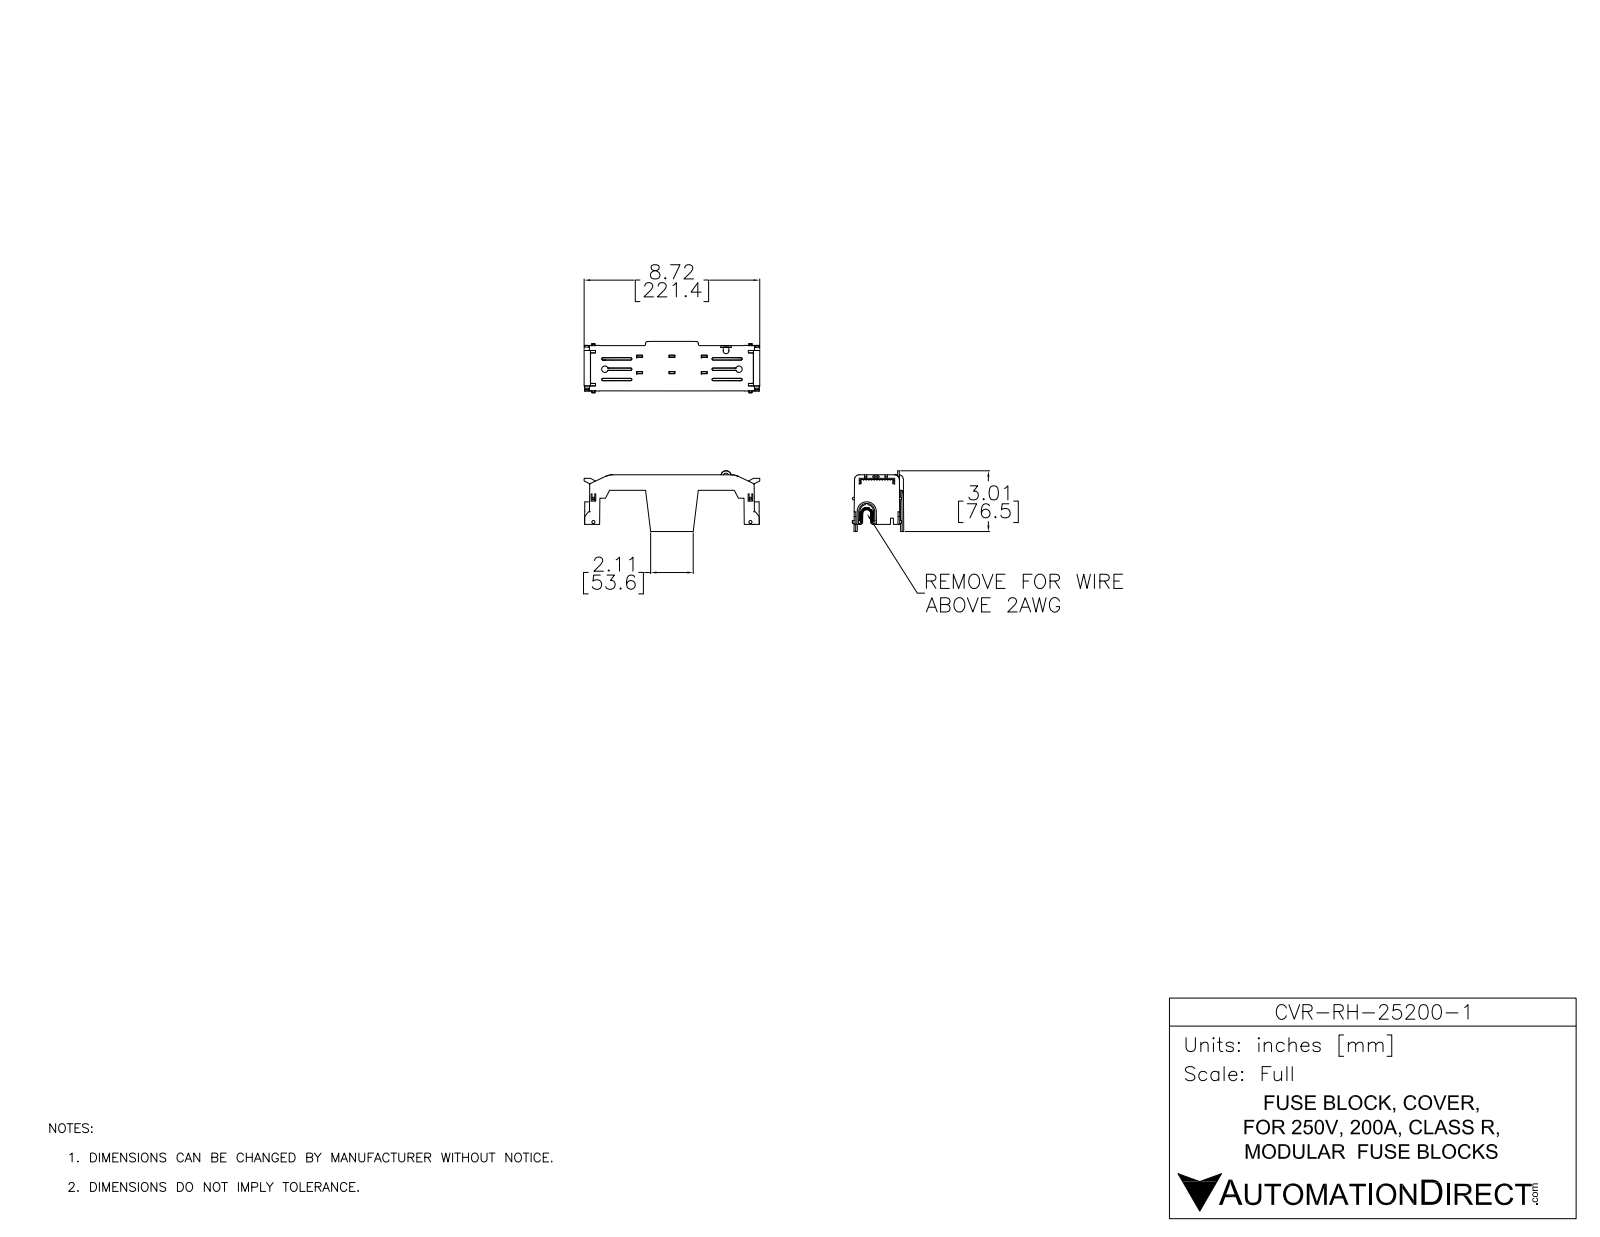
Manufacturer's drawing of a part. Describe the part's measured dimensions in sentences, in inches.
The part is named "CVR-RH-25200-1". Its 3-D file was written by "SolidWorks 2017 (AUTOMOTIVE_DESIGN)". It is 1 solid with 1406 faces: 950 planar, 105 cylindrical and 351 other. Overall it measures 8.715 by 3.012 by 2.554 inches. Its volume is 4.617 cubic inches and its surface area 125 square inches. Round holes: 1 of diameter 0.276. Partial cylindrical surfaces (rounded edges, fillets, slot ends): 16 of radius 0.039, 9 of radius 0.236, 8 of radius 0.118, 7 of radius 0.157, 6 of radius 0.079, 2 of radius 0.01, 2 of radius 0.02, 2 of radius 0.63. The main face-to-face distances are 0.079, 0.197, 0.118, 0.276, 0.803, 0.604, 1.661, 1.74, 1.286, 1.365.
